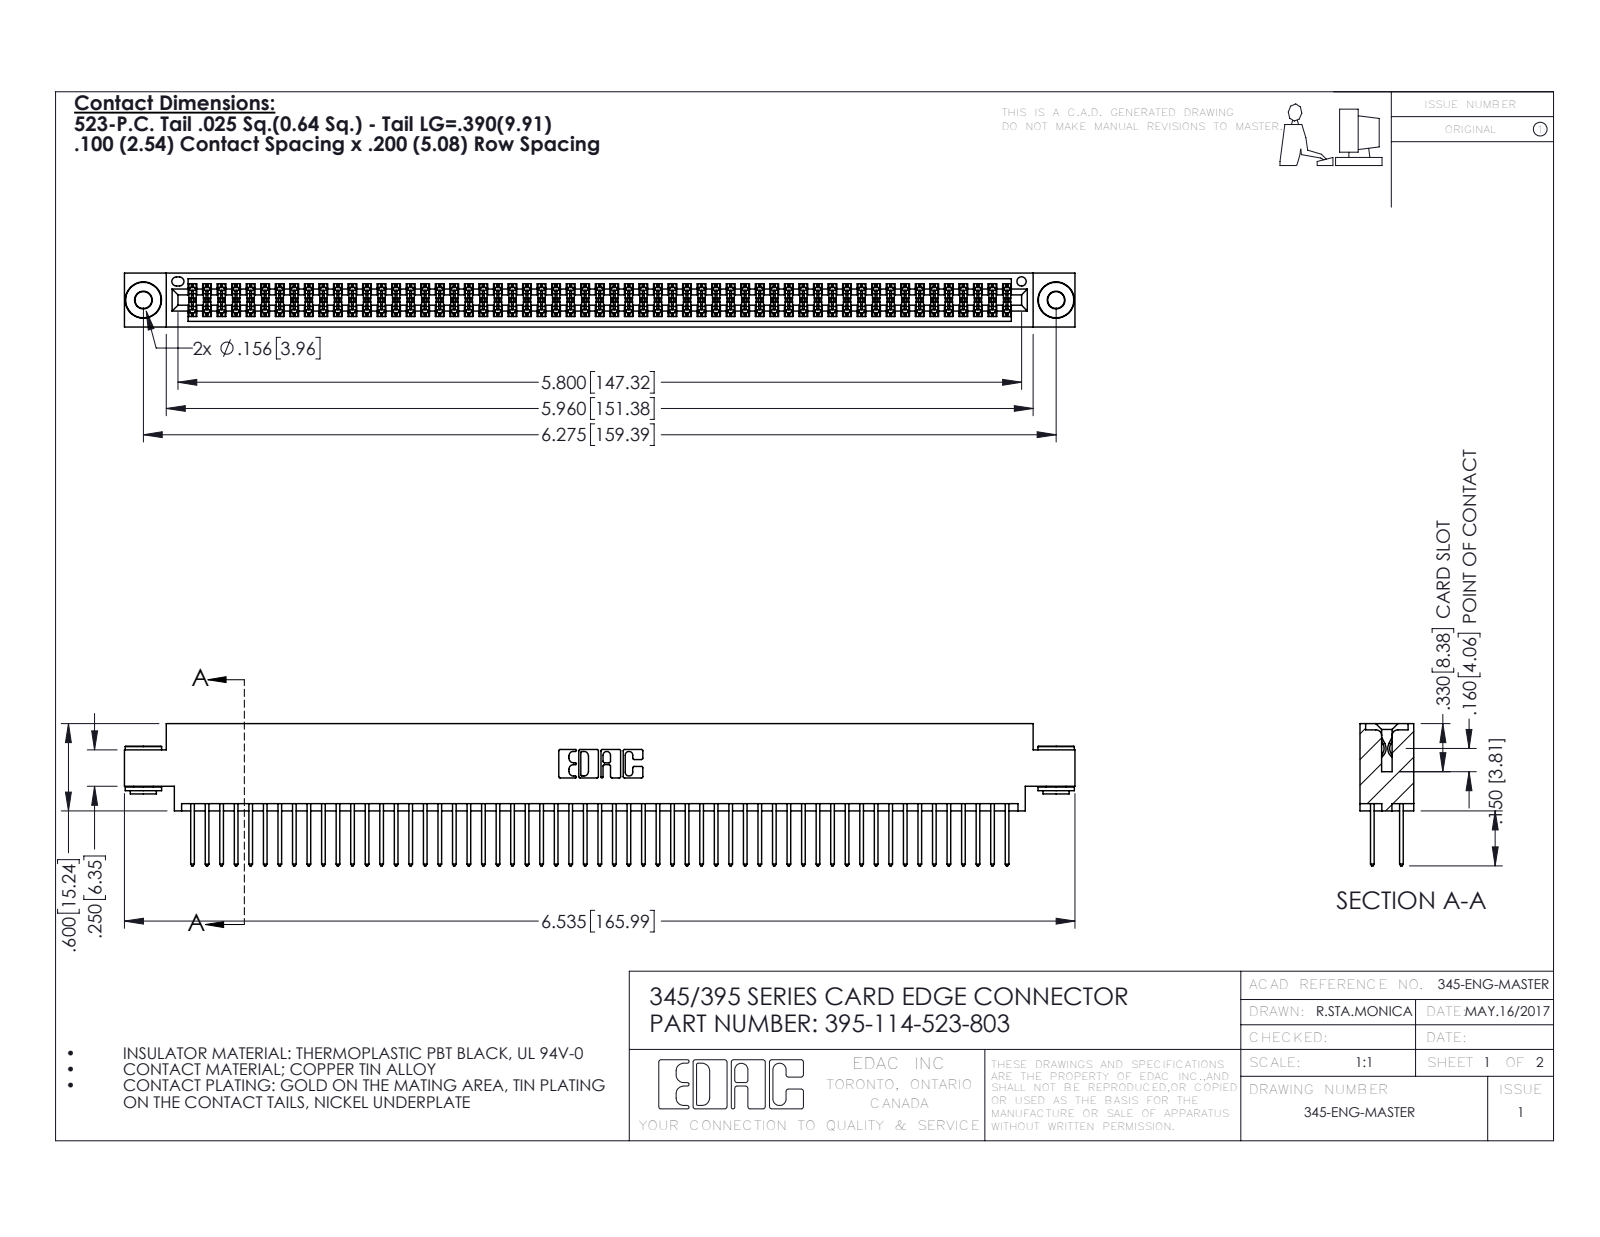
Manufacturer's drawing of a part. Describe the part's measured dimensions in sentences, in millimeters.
The part is named "395-114-523-803; 345-292-001_345-293-123; 345 Part_0.170 Offset - 0.156 Dia-TH; 345-250-002_345-250-002-102". Its 3-D file was written by "SolidWorks 2016 (CONFIG_CONTROL_DESIGN)". It is 117 solids with 5868 faces: 3856 planar, 2004 cylindrical and 8 other. Overall it measures 166 by 24.8 by 9.4 millimeters. Its volume is 16 400 cubic millimeters and its surface area 25 940 square millimeters. Round holes: 2 of diameter 2.9, 2 of diameter 4, 1 of diameter 1.6. Round bosses or shafts: 2 of diameter 6.4, 2 of diameter 4.6, 2 of diameter 3.5. Partial cylindrical surfaces (rounded edges, fillets, slot ends): 171 of radius 0.2, 114 of radius 0.3, 22 of radius 0.3, 6 of radius 0.2, 6 of radius 0.8, 3 of radius 0.7, 2 of radius 0.4, 2 of radius 0.5. The main face-to-face distances are 1.8, 7.6, 5.1, 2.5, 6.9, 0.6, 9.4, 5.7, 4.4, 3.8. The hole center spacings are 6.9, 153.4, 159.4.
